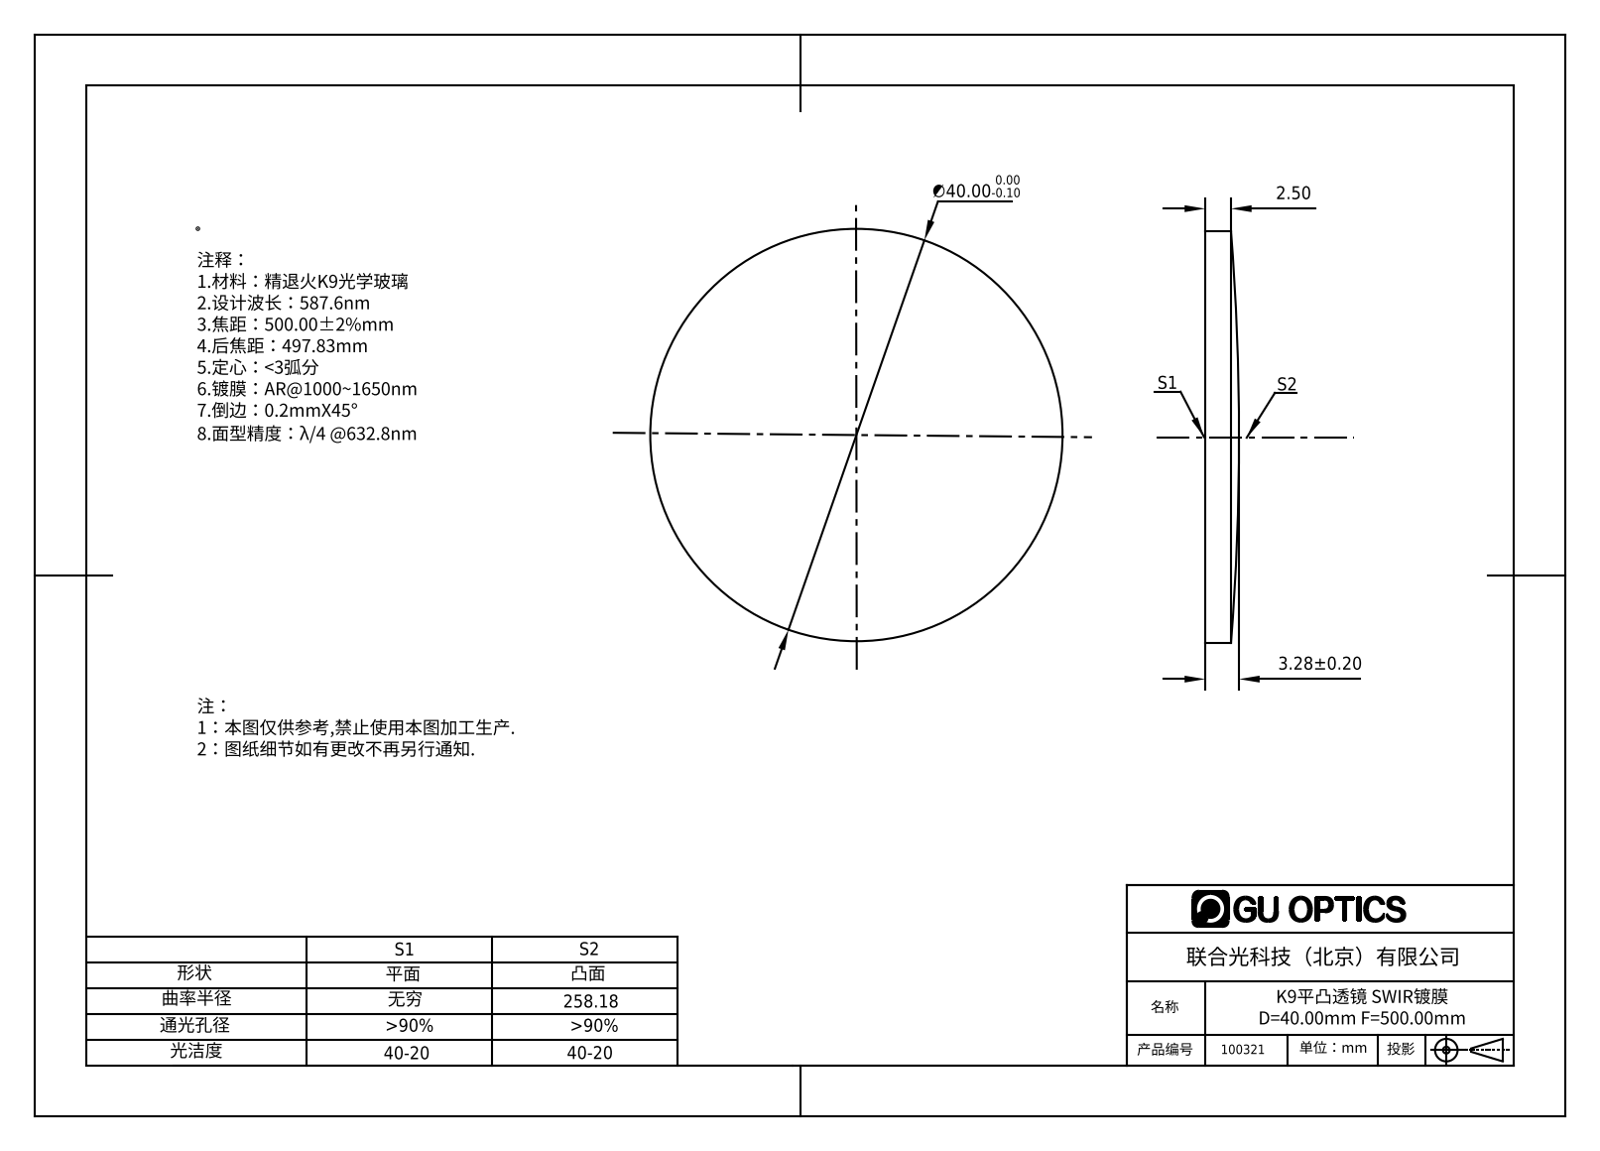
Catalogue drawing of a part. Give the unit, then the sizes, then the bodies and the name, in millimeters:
Units: millimetres
Overall size (bounding box): 40 × 40 × 3.28
Round bosses / shafts (diameter × count): ⌀40 ×1
Volume: 3 632 mm³ · Surface area: 2 829 mm²
Bodies: 1 solid, 5 faces (1 planar, 2 cylindrical, 2 other)
Part name (STEP PRODUCT): 100149
STEP written by: SolidWorks 2016 (AUTOMOTIVE_DESIGN)
